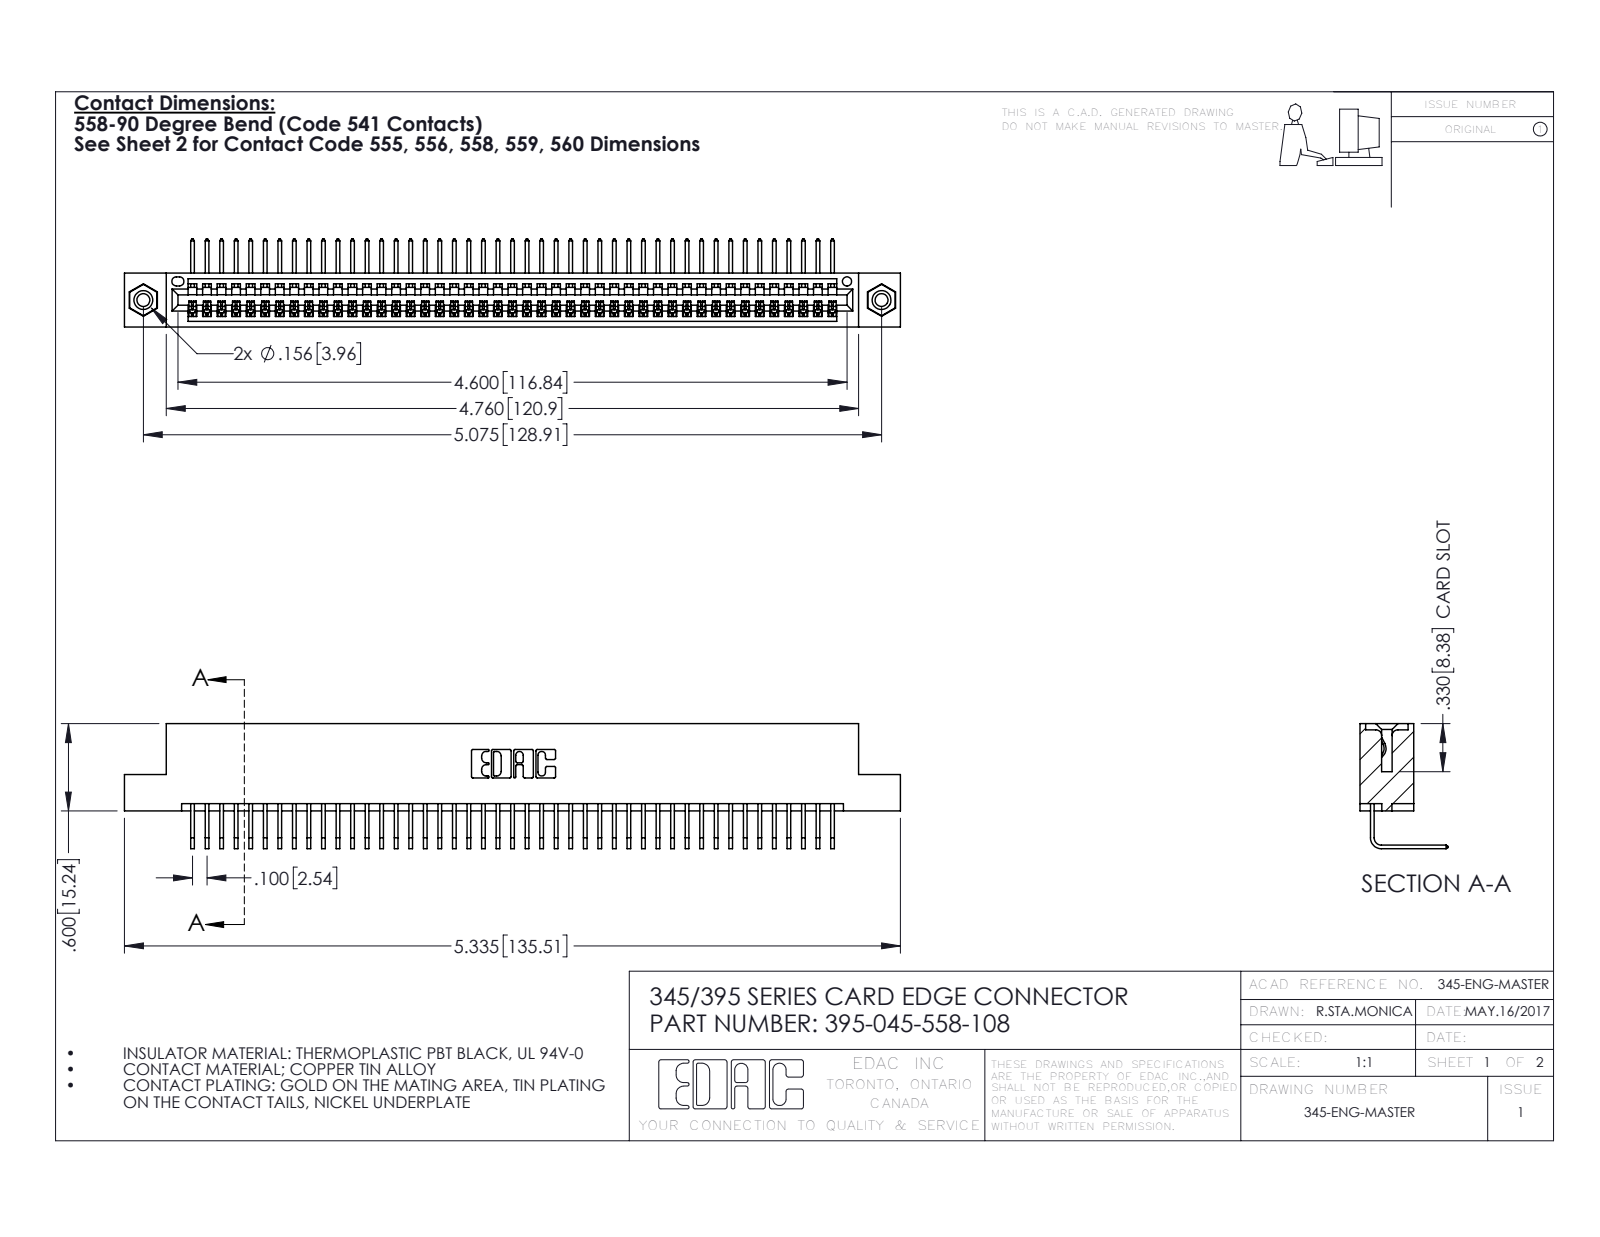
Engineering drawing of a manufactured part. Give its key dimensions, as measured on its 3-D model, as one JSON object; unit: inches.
{"part_name": "345-250-001_345-250-003-102; 395-045-558-108; 345-292-001_558 Tail - 2; 345 Part_Flush Mounting Lugs - 0.156 Dia-TI", "step_written_by": "SolidWorks 2016 (CONFIG_CONTROL_DESIGN)", "units": "inches", "bodies": {"solids": 48, "faces": 2886, "planar": 2002, "cylindrical": 868, "other": 16}, "overall_size": [5.335, 0.859, 0.605], "volume_in3": 0.796, "surface_area_in2": 28.32, "round_holes": [[0.089, 2], [0.125, 2], [0.156, 2], [0.064, 1]], "round_bosses_or_shafts": [[0.155, 2]], "partial_cylinders_radius": [[0.006, 90], [0.01, 22], [0.007, 6], [0.031, 6], [0.026, 3], [0.031, 2], [0.04, 2], [0.014, 1]], "face_to_face_distances": [0.072, 0.298, 0.37, 0.2, 0.098, 0.272, 0.025, 0.225, 0.149, 0.072], "hole_center_spacings": [0.27, 4.839, 5.075]}
